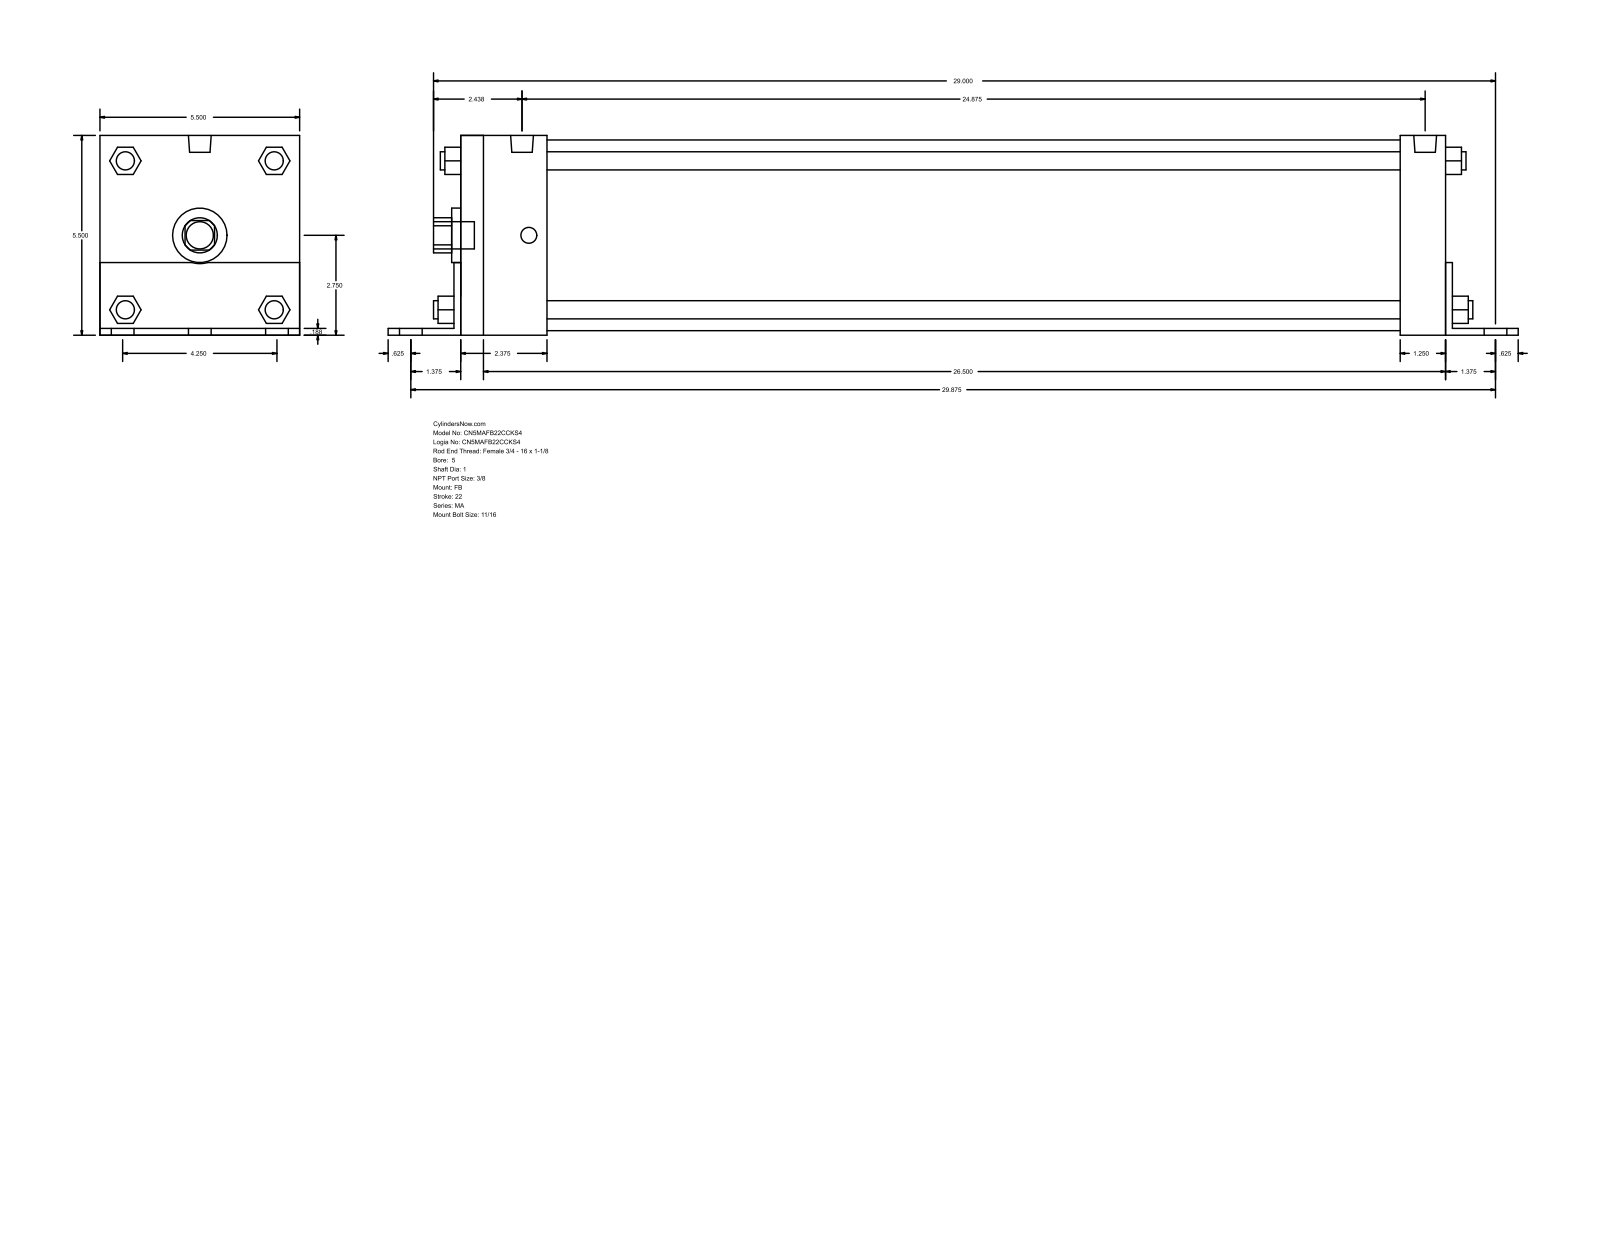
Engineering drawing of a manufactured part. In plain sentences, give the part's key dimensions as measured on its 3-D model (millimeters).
The part is named "MA_FB__0500_1". Its 3-D file was written by "GSSL Pune (CONFIG_CONTROL_DESIGN)". It is 0 solids with 140 faces: 105 planar, 35 cylindrical and 0 other. Overall it measures 790.58 by 139.75 by 139.7 millimeters. Round holes: 1 of diameter 25.4, 1 of diameter 38.1, 1 of diameter 133.35. Round bosses or shafts: 6 of diameter 17.46, 4 of diameter 12.7, 4 of diameter 11.11, 2 of diameter 15.93, 1 of diameter 19.05. Partial cylindrical surfaces (rounded edges, fillets, slot ends): 1 of radius 12.29, 1 of radius 19.81. The main face-to-face distances are 139.7, 4.76, 139.75, 4.71, 134.99, 688.97, 4.77, 693.74, 693.73, 698.5.
